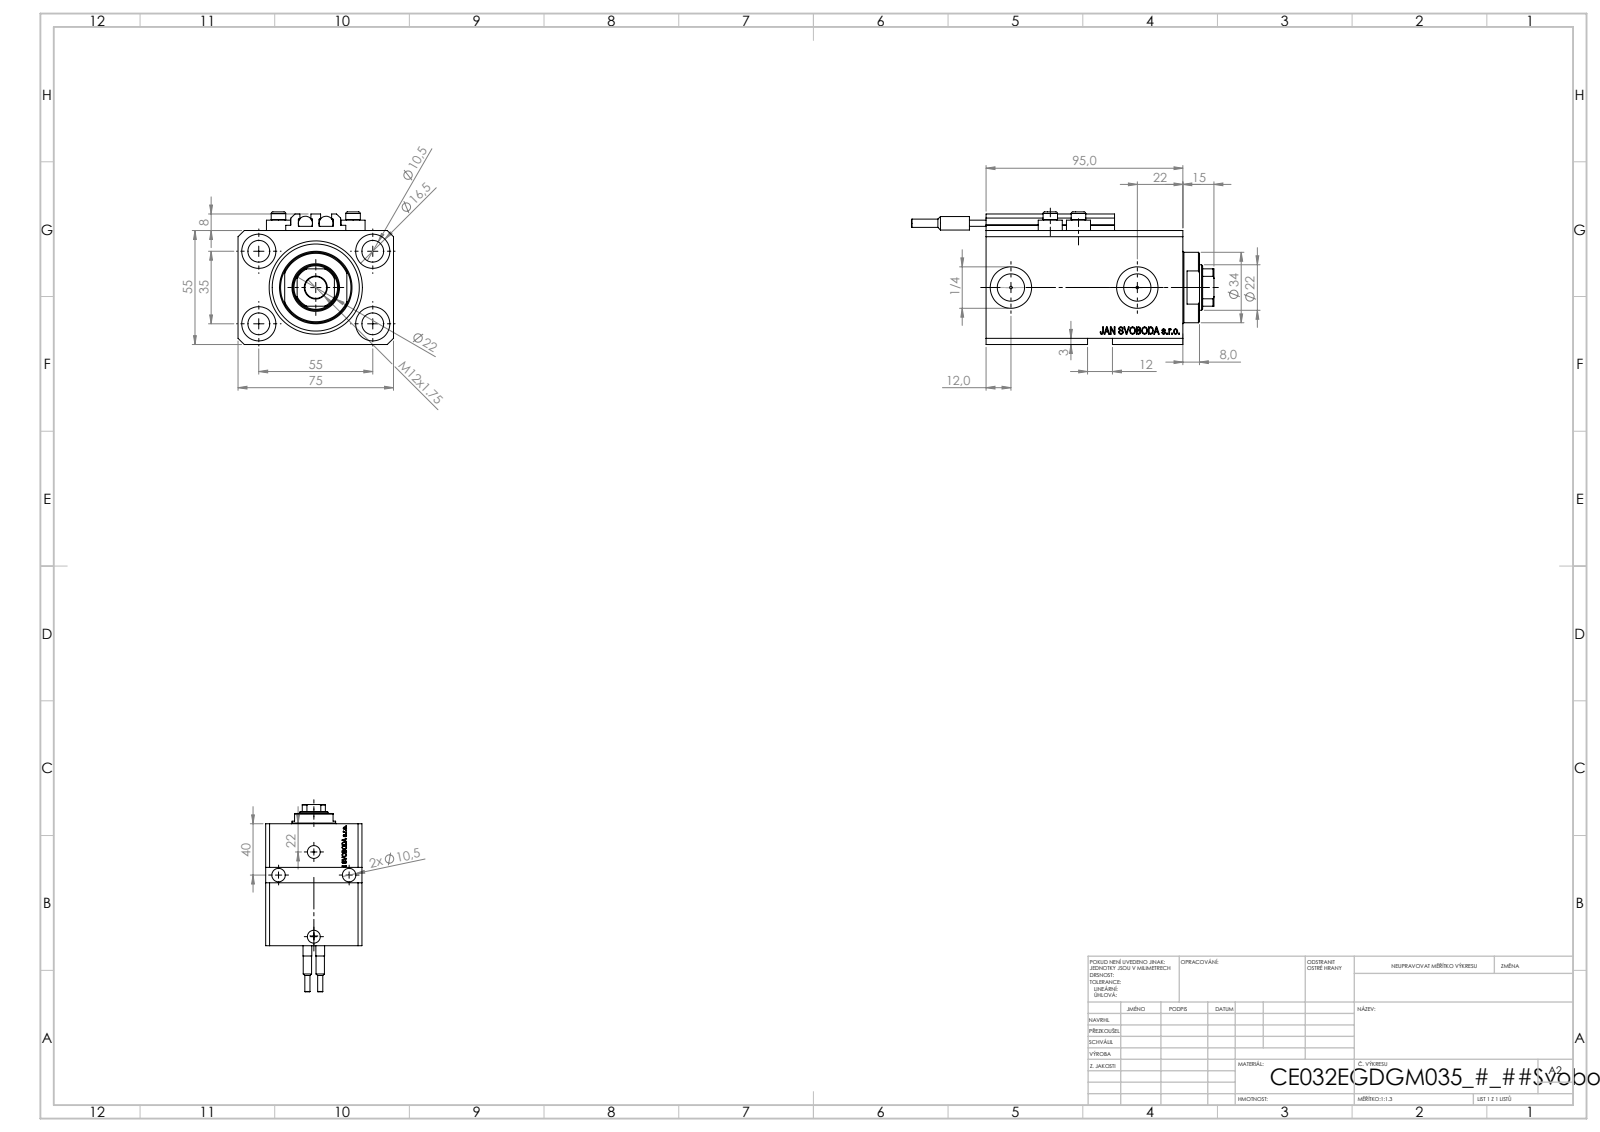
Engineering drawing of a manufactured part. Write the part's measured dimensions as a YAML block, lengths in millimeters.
part_name: "V250CE_E_Body; SWITCH_V250CE; V250CE_VC_E; V250CE_C_VCP (+1 more)"
step_written_by: "SolidWorks 2019 (CONFIG_CONTROL_DESIGN)"
units: millimeters
bodies: {solids: 10, faces: 1132, planar: 550, cylindrical: 150, other: 432}
overall_size: [146, 75, 64]
volume: 335788
surface_area: 88192
round_holes:
  - {diameter: 10.5, count: 7}
  - {diameter: 1.25, count: 4}
  - {diameter: 4, count: 4}
  - {diameter: 16.5, count: 4}
  - {diameter: 10, count: 2}
  - {diameter: 13.16, count: 2}
  - {diameter: 20, count: 2}
  - {diameter: 22, count: 1}
  - {diameter: 32, count: 1}
  - {diameter: 45, count: 1}
round_bosses_or_shafts:
  - {diameter: 11.6, count: 4}
  - {diameter: 7, count: 4}
  - {diameter: 6.8, count: 2}
  - {diameter: 6.5, count: 2}
  - {diameter: 4, count: 2}
  - {diameter: 34, count: 1}
partial_cylinders:
  - {radius: 0.2, count: 10}
  - {radius: 10.5, count: 1}
face_to_face_distances: [55, 75, 3, 15, 95, 80, 9.9, 57, 70.1, 85.1]
hole_center_spacings: [32.6, 55, 13.6, 14.09, 25.81, 29.58, 30, 32.87]
